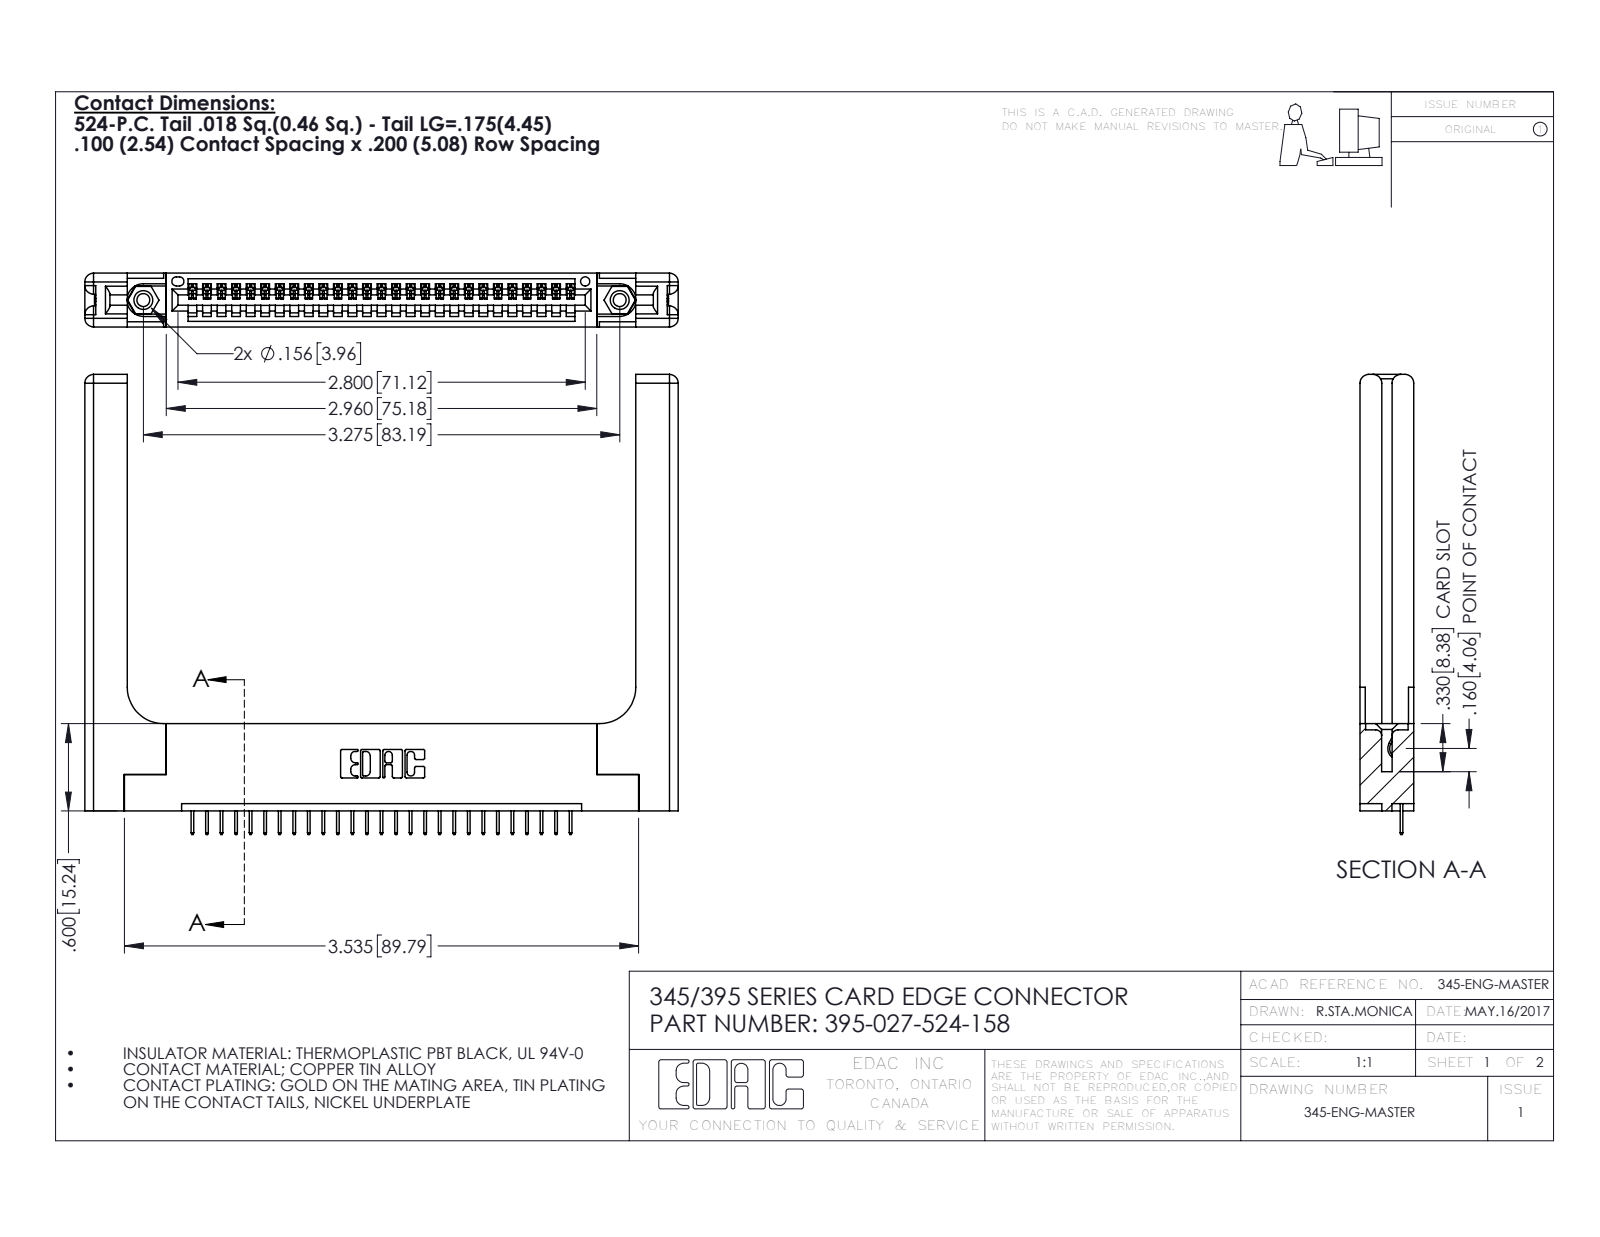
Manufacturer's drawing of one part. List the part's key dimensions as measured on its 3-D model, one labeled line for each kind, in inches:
Part name (STEP PRODUCT): 345-250-001_345-250-001-102; 395-027-524-158; 345-220-058_345-220-058; 345-292-001_345-293-124 (+1 more)
STEP written by: SolidWorks 2016 (CONFIG_CONTROL_DESIGN)
Units: inches
Bodies: 32 solids, 2056 faces (1470 planar, 526 cylindrical, 60 other)
Overall size (bounding box): 4.079 × 3.162 × 0.37
Volume: 1.106 in³ · Surface area: 27.18 in²
Round holes (diameter × count): ⌀0.089 ×2, ⌀0.125 ×2, ⌀0.156 ×2, ⌀0.064 ×1
Round bosses / shafts (diameter × count): ⌀0.155 ×2
Partial cylindrical surfaces — rounded edges, fillets, slot ends (radius × count): R0.006 ×54, R0.01 ×22, R0.06 ×16, R0.007 ×6, R0.031 ×6, R0.026 ×3, R0.03 ×2, R0.031 ×2
Main face-to-face distances: 0.37, 0.072, 0.298, 0.2, 0.148, 0.15, 0.077, 0.22, 0.098, 0.272
Hole centre spacings: 0.27, 3.04, 3.275
